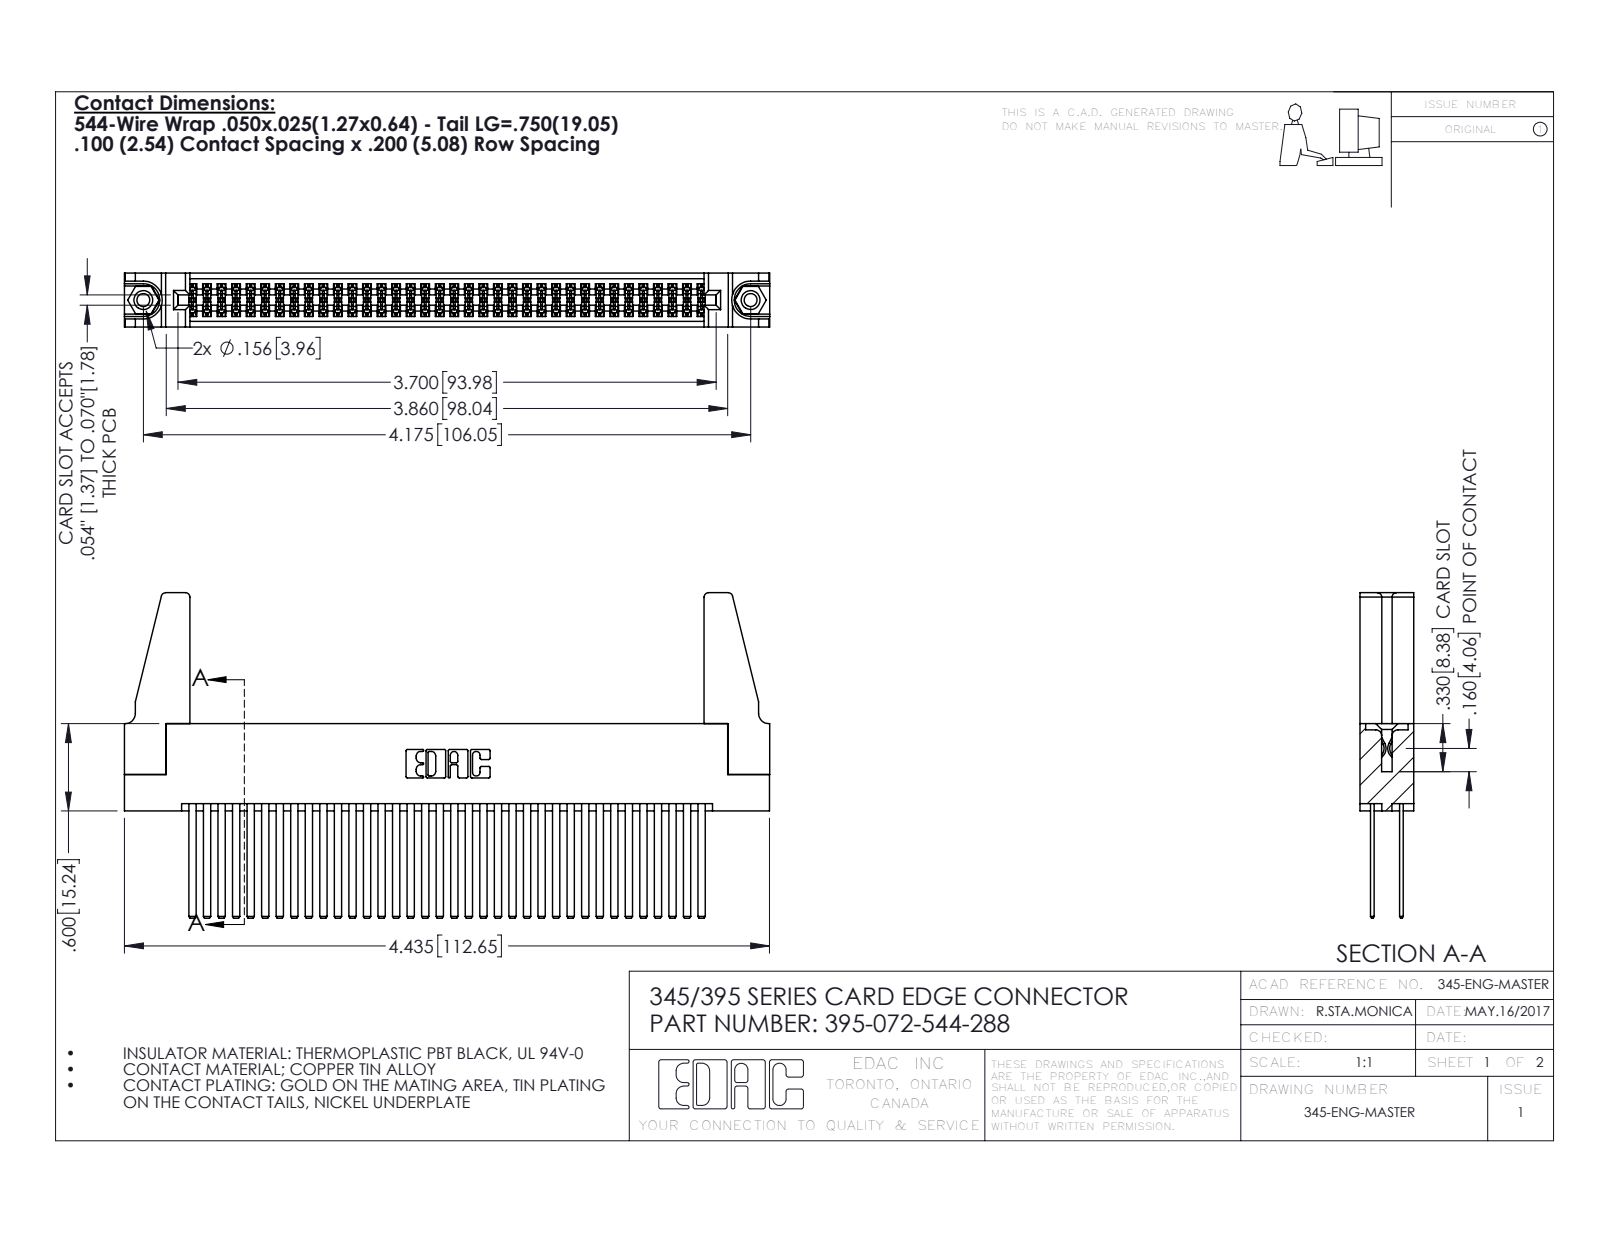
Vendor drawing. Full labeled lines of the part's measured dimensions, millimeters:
Part name (STEP PRODUCT): 345 Part_Flush Mounting Lugs - 0.156 Dia-TH; 345-292-001_345-293-144; 395-072-544-288; 345-250-001_345-250-001-102 (+1 more)
STEP written by: SolidWorks 2016 (CONFIG_CONTROL_DESIGN)
Units: millimetres
Bodies: 77 solids, 3418 faces (2240 planar, 1162 cylindrical, 16 other)
Overall size (bounding box): 112.7 × 56.8 × 9.4
Volume: 15 200 mm³ · Surface area: 23 550 mm²
Round holes (diameter × count): ⌀2.3 ×2, ⌀3.2 ×2, ⌀4 ×2, ⌀1.6 ×1
Round bosses / shafts (diameter × count): ⌀3.9 ×2
Partial cylindrical surfaces — rounded edges, fillets, slot ends (radius × count): R0.2 ×108, R0.3 ×22, R0.8 ×8, R0.2 ×6, R0.8 ×6, R0.7 ×3, R0.4 ×2, R0.5 ×2
Main face-to-face distances: 1.8, 7.6, 5.1, 2.5, 6.9, 0.6, 5.7, 9.4, 4.4, 1.3
Hole centre spacings: 6.9, 100.1, 106
